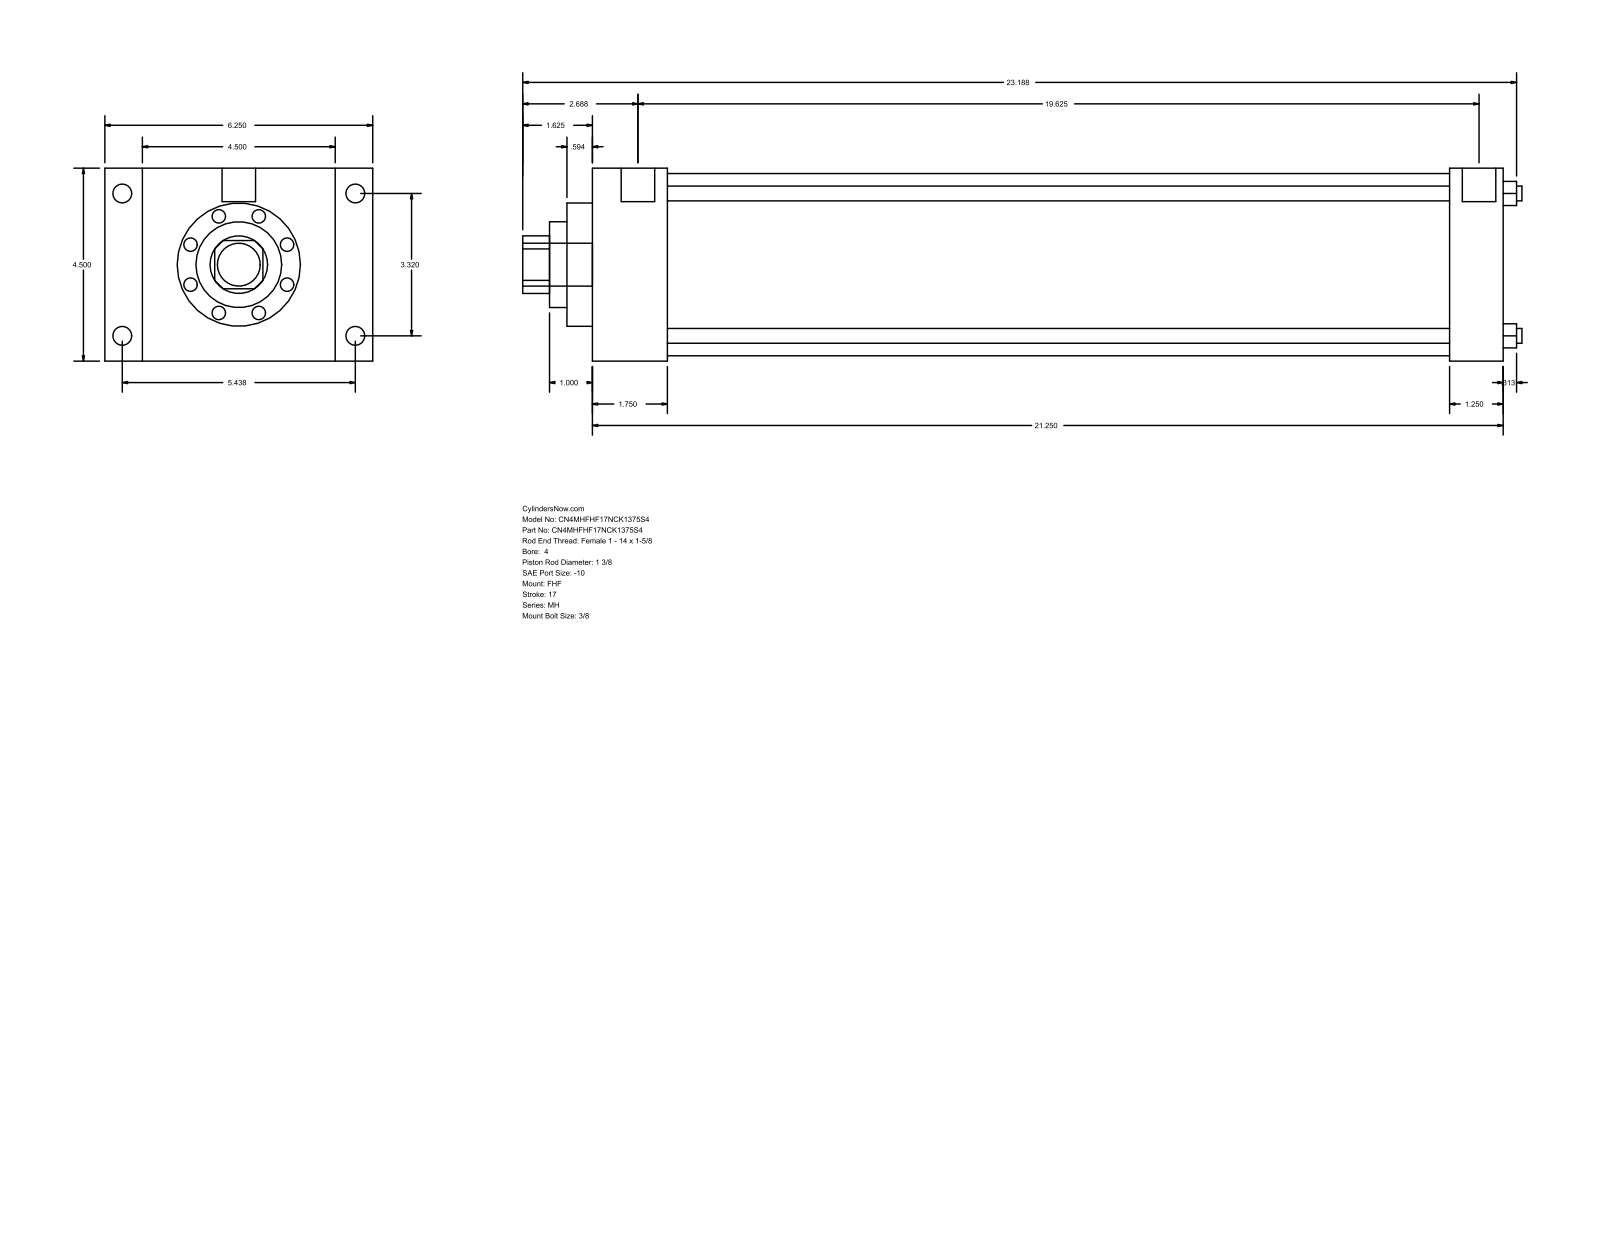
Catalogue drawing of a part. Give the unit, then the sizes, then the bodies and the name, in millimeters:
Units: millimetres
Overall size (bounding box): 592.14 × 158.75 × 114.3
Round holes (diameter × count): ⌀8.76 ×4, ⌀34.92 ×1, ⌀50.8 ×1, ⌀73.03 ×1, ⌀107.95 ×1
Round bosses / shafts (diameter × count): ⌀11.13 ×4, ⌀8.73 ×4, ⌀19.84 ×2, ⌀25.4 ×1
Partial cylindrical surfaces — rounded edges, fillets, slot ends (radius × count): R17.06 ×1
Main face-to-face distances: 114.3, 539.75, 44.45, 495.3, 22.23, 136.53, 158.76, 508, 463.55, 31.75
Hole centre spacings: 59.62, 84.32, 119.25
Bodies: 0 solids, 90 faces (61 planar, 29 cylindrical, 0 other)
Part name (STEP PRODUCT): MH_FHF__0400_1.375
STEP written by: GSSL Pune (CONFIG_CONTROL_DESIGN)
